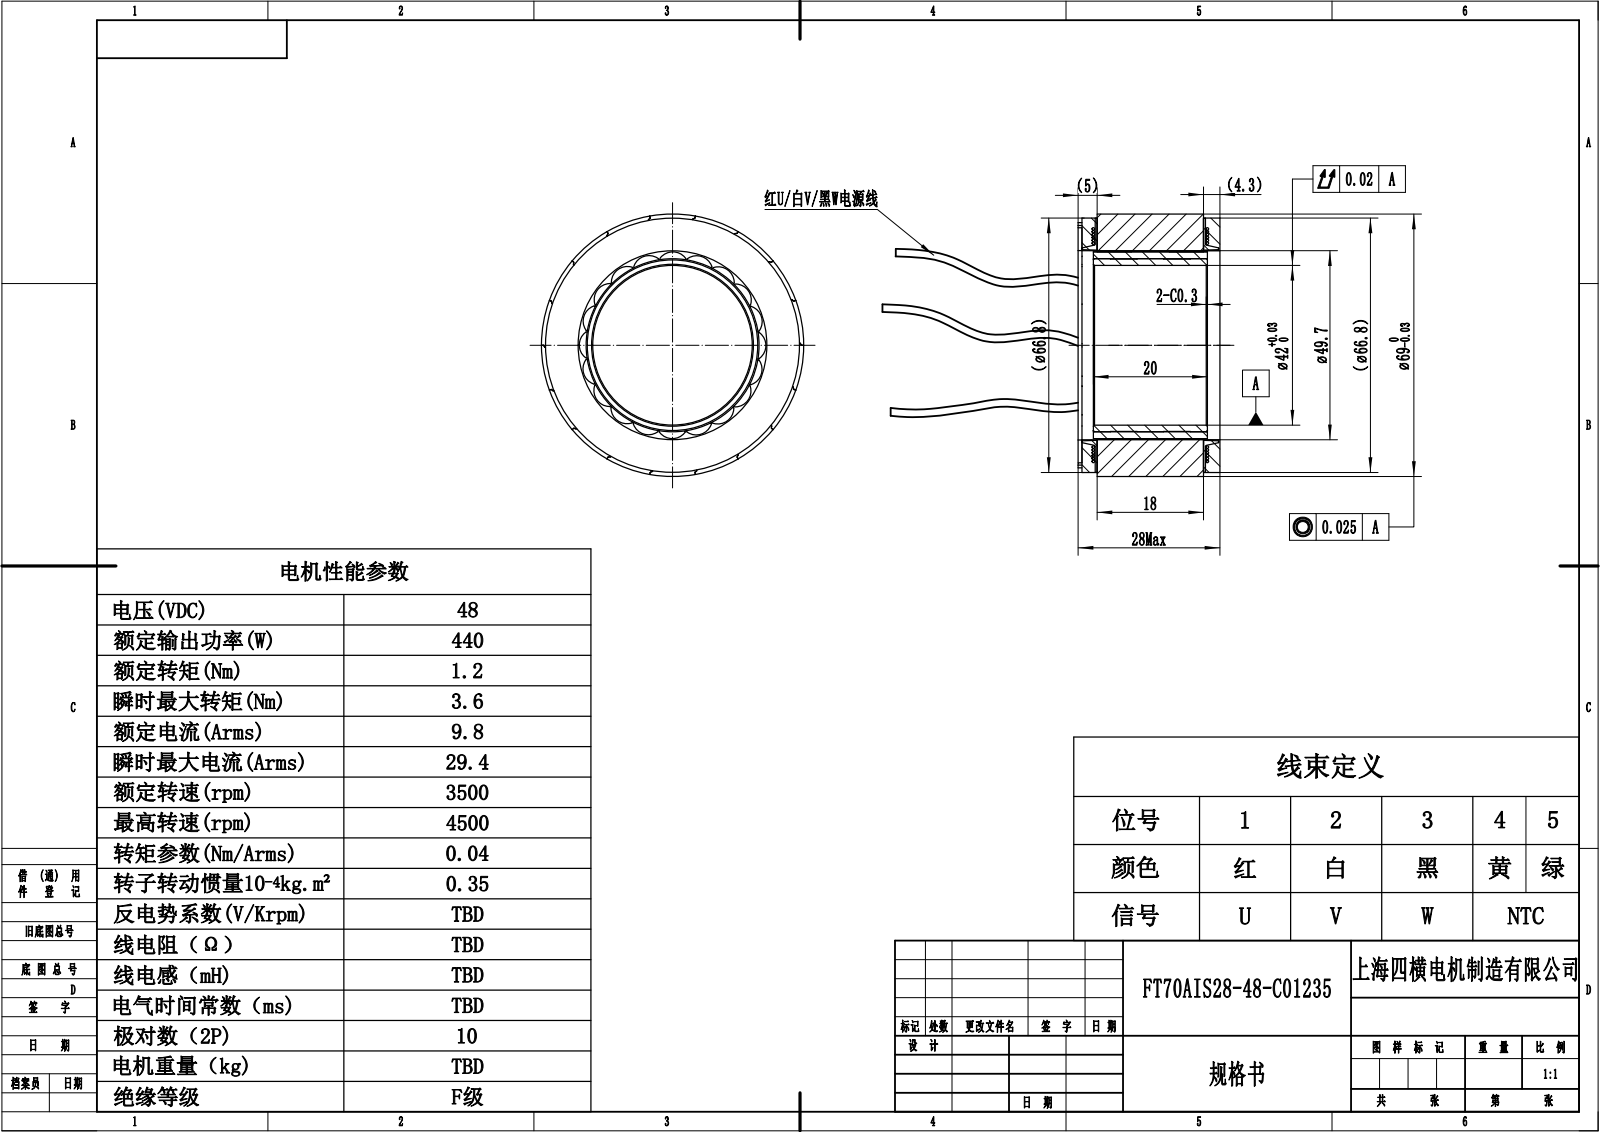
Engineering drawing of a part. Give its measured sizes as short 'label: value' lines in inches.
name: 70-h10; 70定子铁芯H10; FT70AIS28-48-C01235; 01.A005.000141 70无框转子铁芯H13 (+7 more)
written by: SolidWorks 2024 (CONFIG_CONTROL_DESIGN)
unit: in
bodies: 186 solids, 8753 faces (1952 planar, 3193 cylindrical, 3608 other)
size: 2.728 × 2.722 × 0.76
volume: 2.085 in³; area: 85.46 in²
holes: 3× ⌀0.059, 1× ⌀1.654, 1× ⌀1.791, 1× ⌀1.957, 1× ⌀1.961
bosses: 432× ⌀0.03, 1× ⌀2.728, 1× ⌀2.634, 1× ⌀2.63, 1× ⌀2.535, 1× ⌀1.783
rounds: 316× R0.02, 274× R0.006, 180× R0.008, 140× R0.004, 74× R0.012, 72× R0.01, 60× R0.014, 40× R0.079
face distances: 0.394, 0.157, 0.551, 0.039, 0.992, 0.197, 0.72, 0.563, 0.169, 0.872
hole spacings: 1.181, 0.611, 1.181
